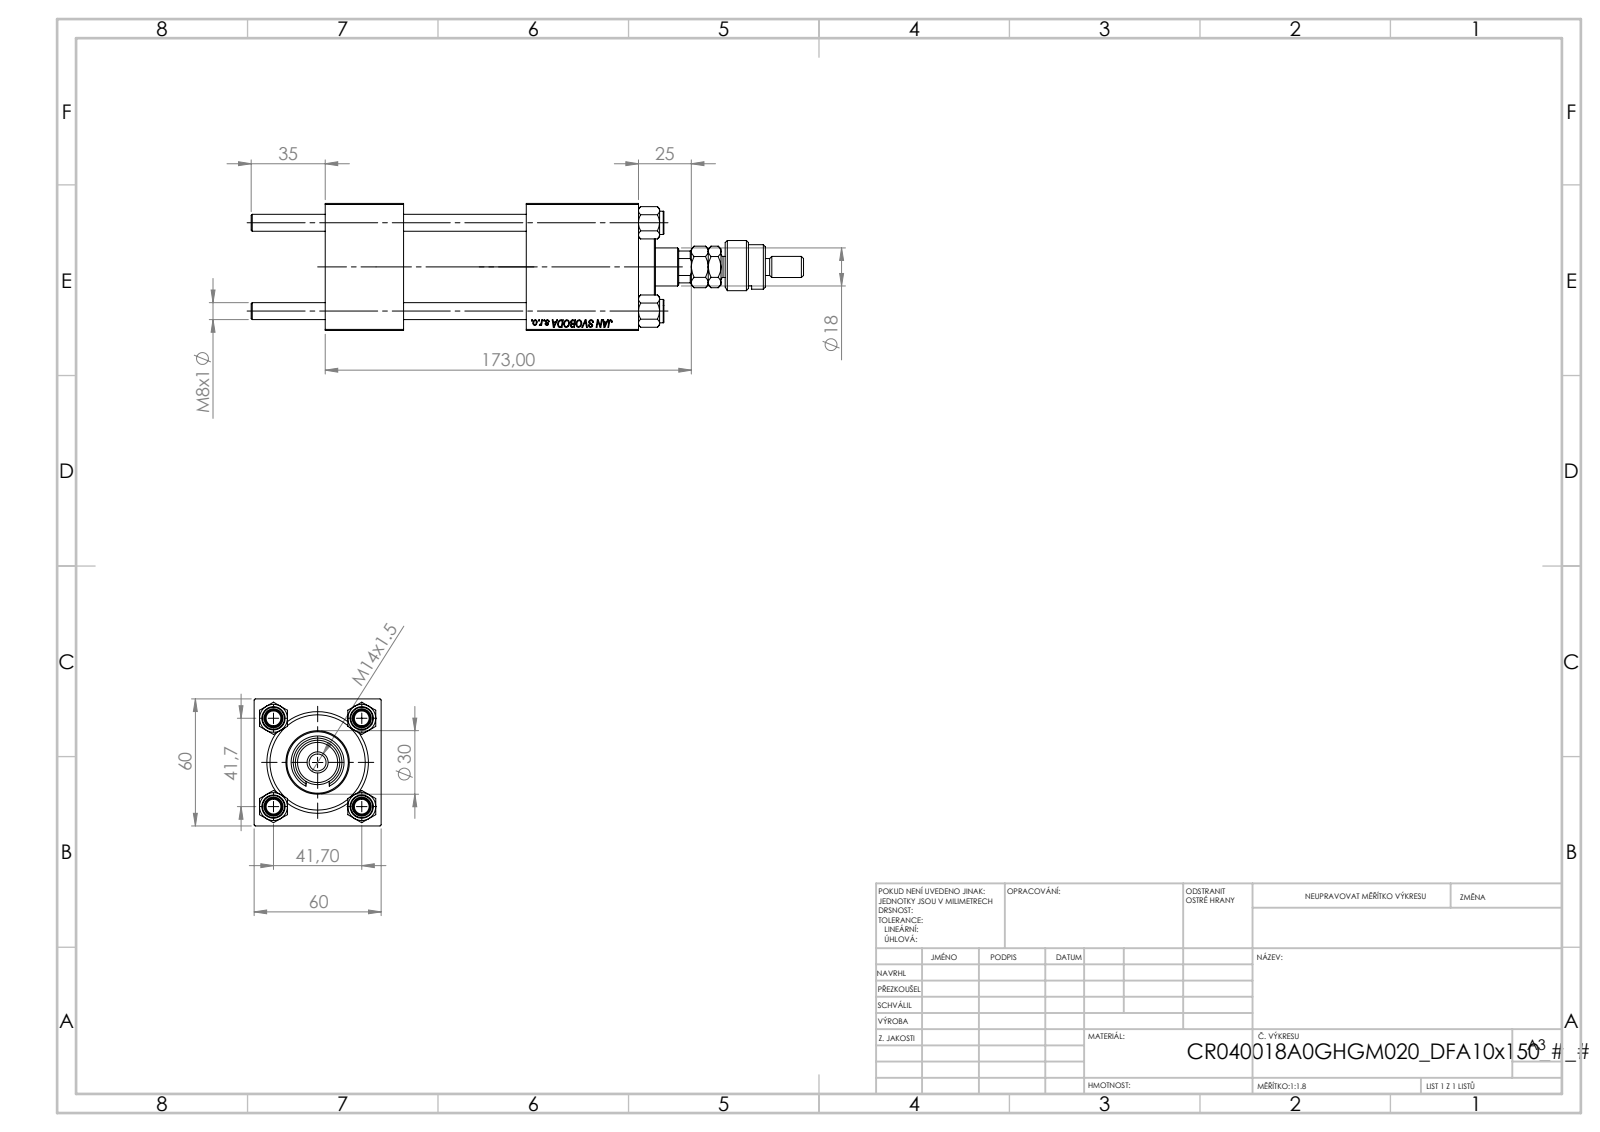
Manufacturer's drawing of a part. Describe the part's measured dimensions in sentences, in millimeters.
The part is named "V215CR_BODY_A; FEMALE_PART_FOR_DFA; V215_VC_A; NUT_M5 (+3 more)". Its 3-D file was written by "SolidWorks 2019 (CONFIG_CONTROL_DESIGN)". It is 13 solids with 1220 faces: 549 planar, 91 cylindrical and 580 other. Overall it measures 261 by 60 by 60 millimeters. Its volume is 425 694 cubic millimeters and its surface area 119 451 square millimeters. Round holes: 4 of diameter 8, 2 of diameter 7, 2 of diameter 16.66, 2 of diameter 24, 1 of diameter 8.5, 1 of diameter 18, 1 of diameter 21, 1 of diameter 31, 1 of diameter 40, 1 of diameter 45. Round bosses or shafts: 4 of diameter 11, 1 of diameter 46, 1 of diameter 30, 1 of diameter 25, 1 of diameter 16, 1 of diameter 10, 1 of diameter 8. Partial cylindrical surfaces (rounded edges, fillets, slot ends): 1 of radius 5.5, 1 of radius 8.5, 1 of radius 8.75. The main face-to-face distances are 60, 37, 148, 111, 53, 58, 95, 119.3, 82.3, 24.3. The hole center spacings are 29.49, 41.7, 58.97, 92.5.
